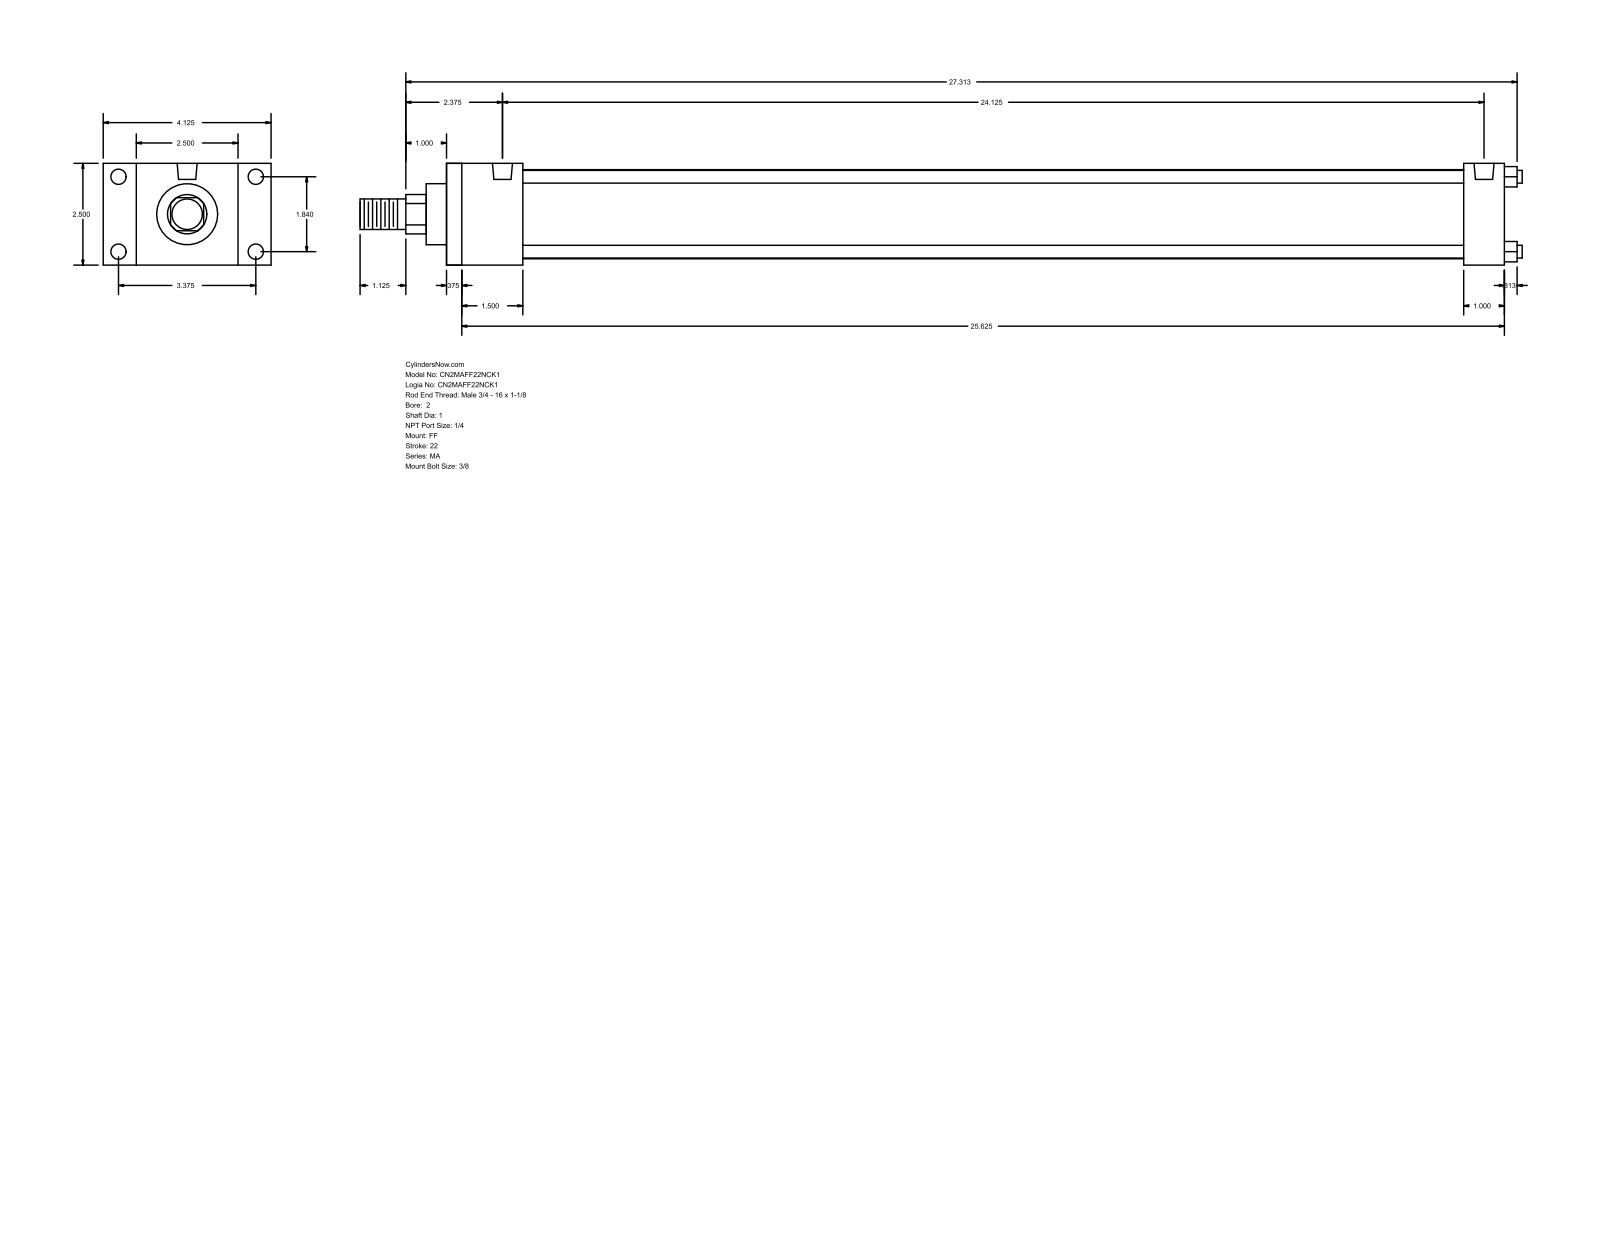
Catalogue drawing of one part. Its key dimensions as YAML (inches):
part_name: "MA_FF__0200_1"
step_written_by: "GSSL Pune (CONFIG_CONTROL_DESIGN)"
units: inches
bodies: {solids: 0, faces: 92, planar: 64, cylindrical: 28, other: 0}
overall_size: [28.563, 4.125, 2.5]
round_holes:
  - {diameter: 0.313, count: 4}
  - {diameter: 0.375, count: 4}
  - {diameter: 0.492, count: 2}
round_bosses_or_shafts:
  - {diameter: 0.313, count: 4}
  - {diameter: 2.19, count: 1}
  - {diameter: 1.5, count: 1}
  - {diameter: 1, count: 1}
  - {diameter: 0.75, count: 1}
partial_cylinders:
  - {radius: 0.484, count: 1}
face_to_face_distances: [2.5, 26, 0.375, 25.625, 1, 0.813, 0.5, 1.875, 25, 1.5]
hole_center_spacings: [1.84, 3.375, 3.844, 24.125]
